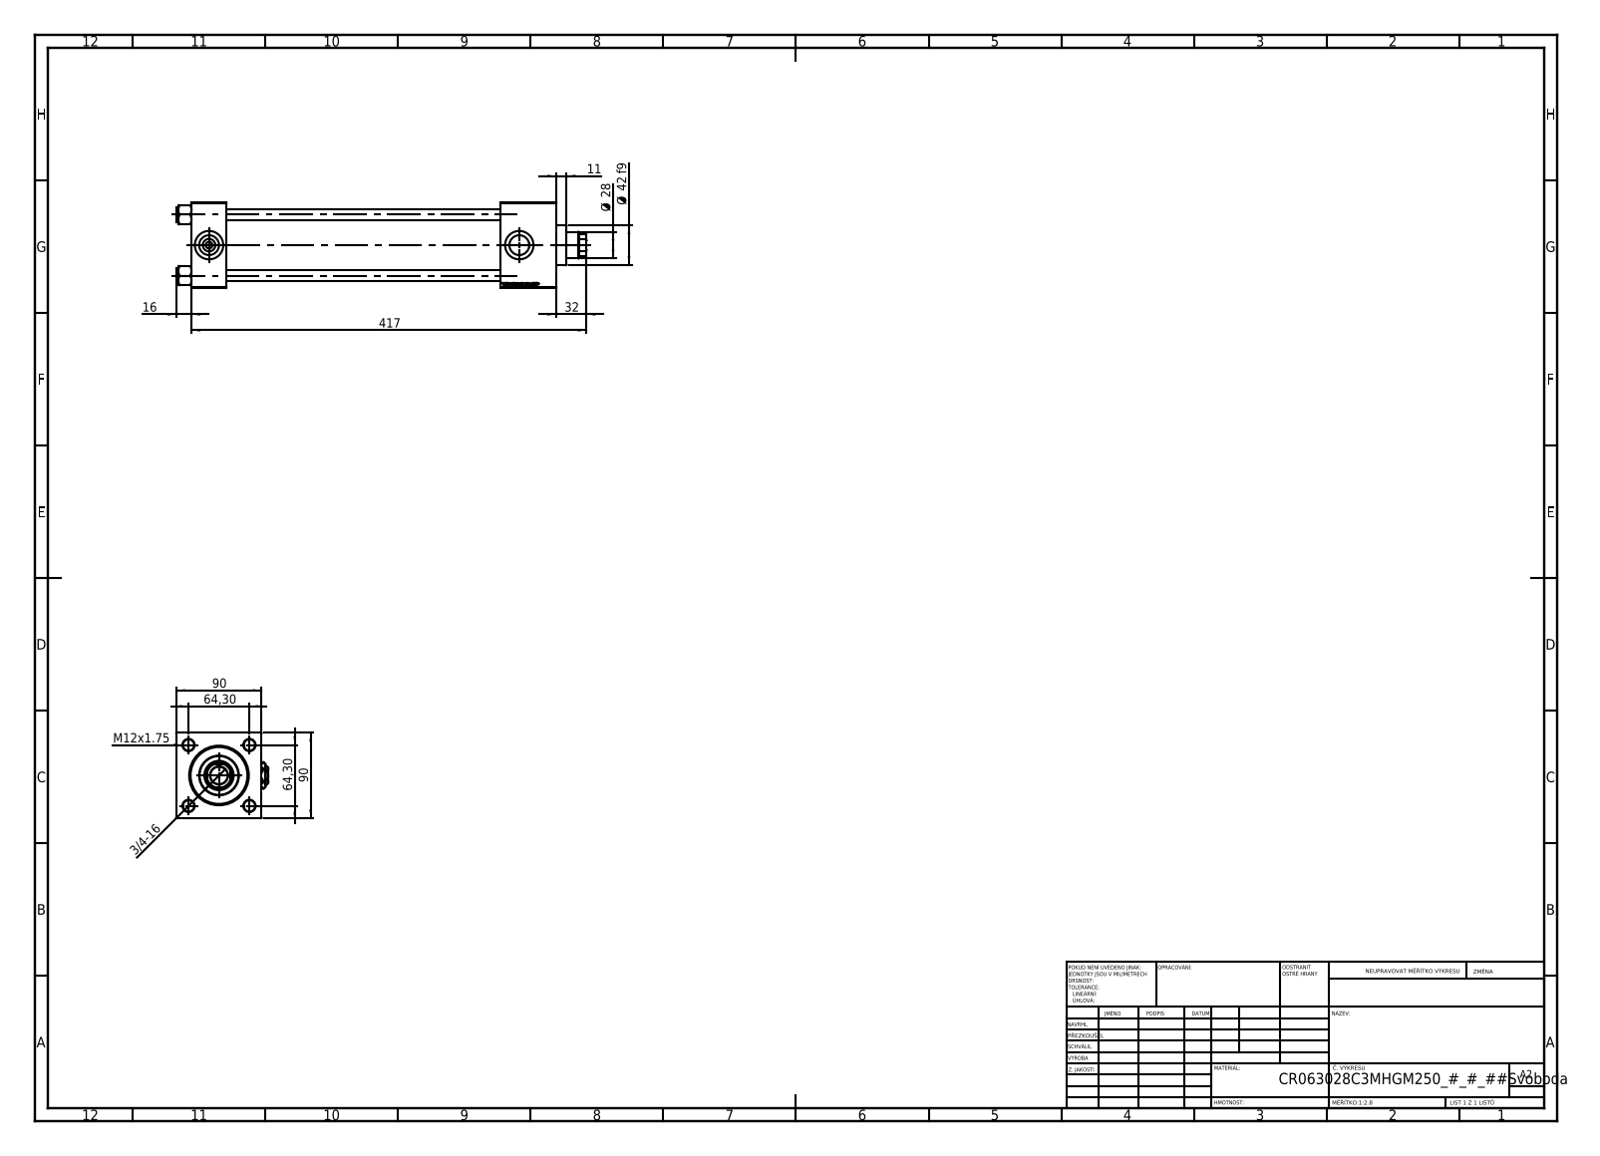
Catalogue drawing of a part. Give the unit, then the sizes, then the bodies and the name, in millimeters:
Units: millimetres
Overall size (bounding box): 433 × 97 × 90
Round holes (diameter × count): ⌀12 ×4, ⌀7 ×2, ⌀20.96 ×2, ⌀30 ×2, ⌀18.5 ×1, ⌀28 ×1, ⌀31 ×1, ⌀50 ×1, ⌀60 ×1, ⌀63 ×1
Round bosses / shafts (diameter × count): ⌀15 ×4, ⌀69 ×1, ⌀42 ×1
Partial cylindrical surfaces — rounded edges, fillets, slot ends (radius × count): R13.5 ×1
Main face-to-face distances: 90, 37, 348, 385, 59, 326, 289, 356.3, 319.3, 30.3
Hole centre spacings: 45.47, 64.3, 90.93, 327.5
Volume: 1 329 000 mm³ · Surface area: 334 209 mm²
Bodies: 13 solids, 1250 faces (574 planar, 98 cylindrical, 578 other)
Part name (STEP PRODUCT): V215CR_VCP_C; NUT_M5_C; Zatka_pro_OIL_PORT; V215_VC_A (+2 more)
STEP written by: SolidWorks 2019 (CONFIG_CONTROL_DESIGN)
